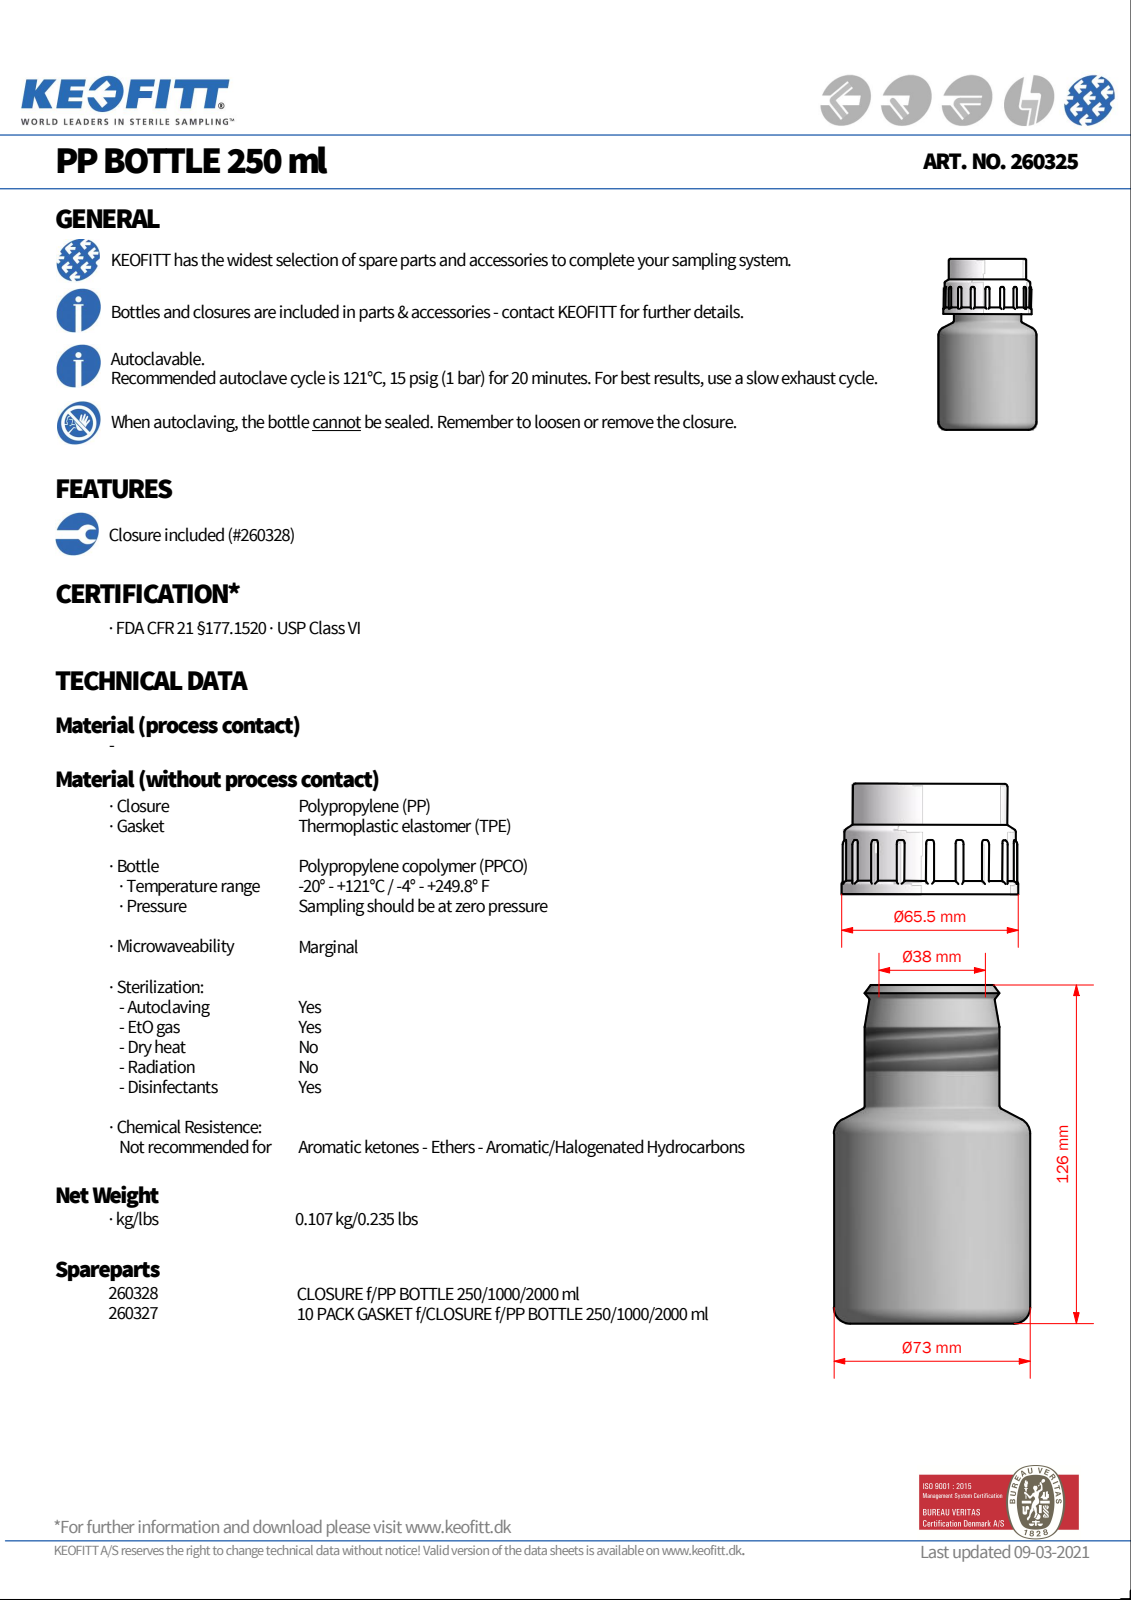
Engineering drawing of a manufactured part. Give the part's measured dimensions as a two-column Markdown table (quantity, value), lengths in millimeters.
| quantity | value |
| --- | --- |
| part name | 260325 |
| STEP written by | Autodesk Inventor 2022 (AUTOMOTIVE_DESIGN) |
| units | millimeters |
| bodies | 3 solids, 264 faces (81 planar, 48 cylindrical, 135 other) |
| overall size | 127.13 × 72.8 × 72.8 |
| volume | 117 854 mm³ |
| surface area | 83 236 mm² |
| round holes (diameter × count) | 43.4 × 1, 53.4 × 1, 54.8 × 1, 59.7 × 1, 61.5 × 1, 66.2 × 1 |
| round bosses / shafts (diameter × count) | 72.8 × 1, 65.5 × 1, 63.7 × 1, 57.4 × 1, 50 × 1 |
| partial cylindrical surfaces (radius × count) | 0.8 × 36 |
| main face-to-face distances | 3.3, 2, 39, 41, 125.07, 121.77, 121.42, 118.12, 3.65, 37 |
| hole center spacings | 0.59, 0.6 |
